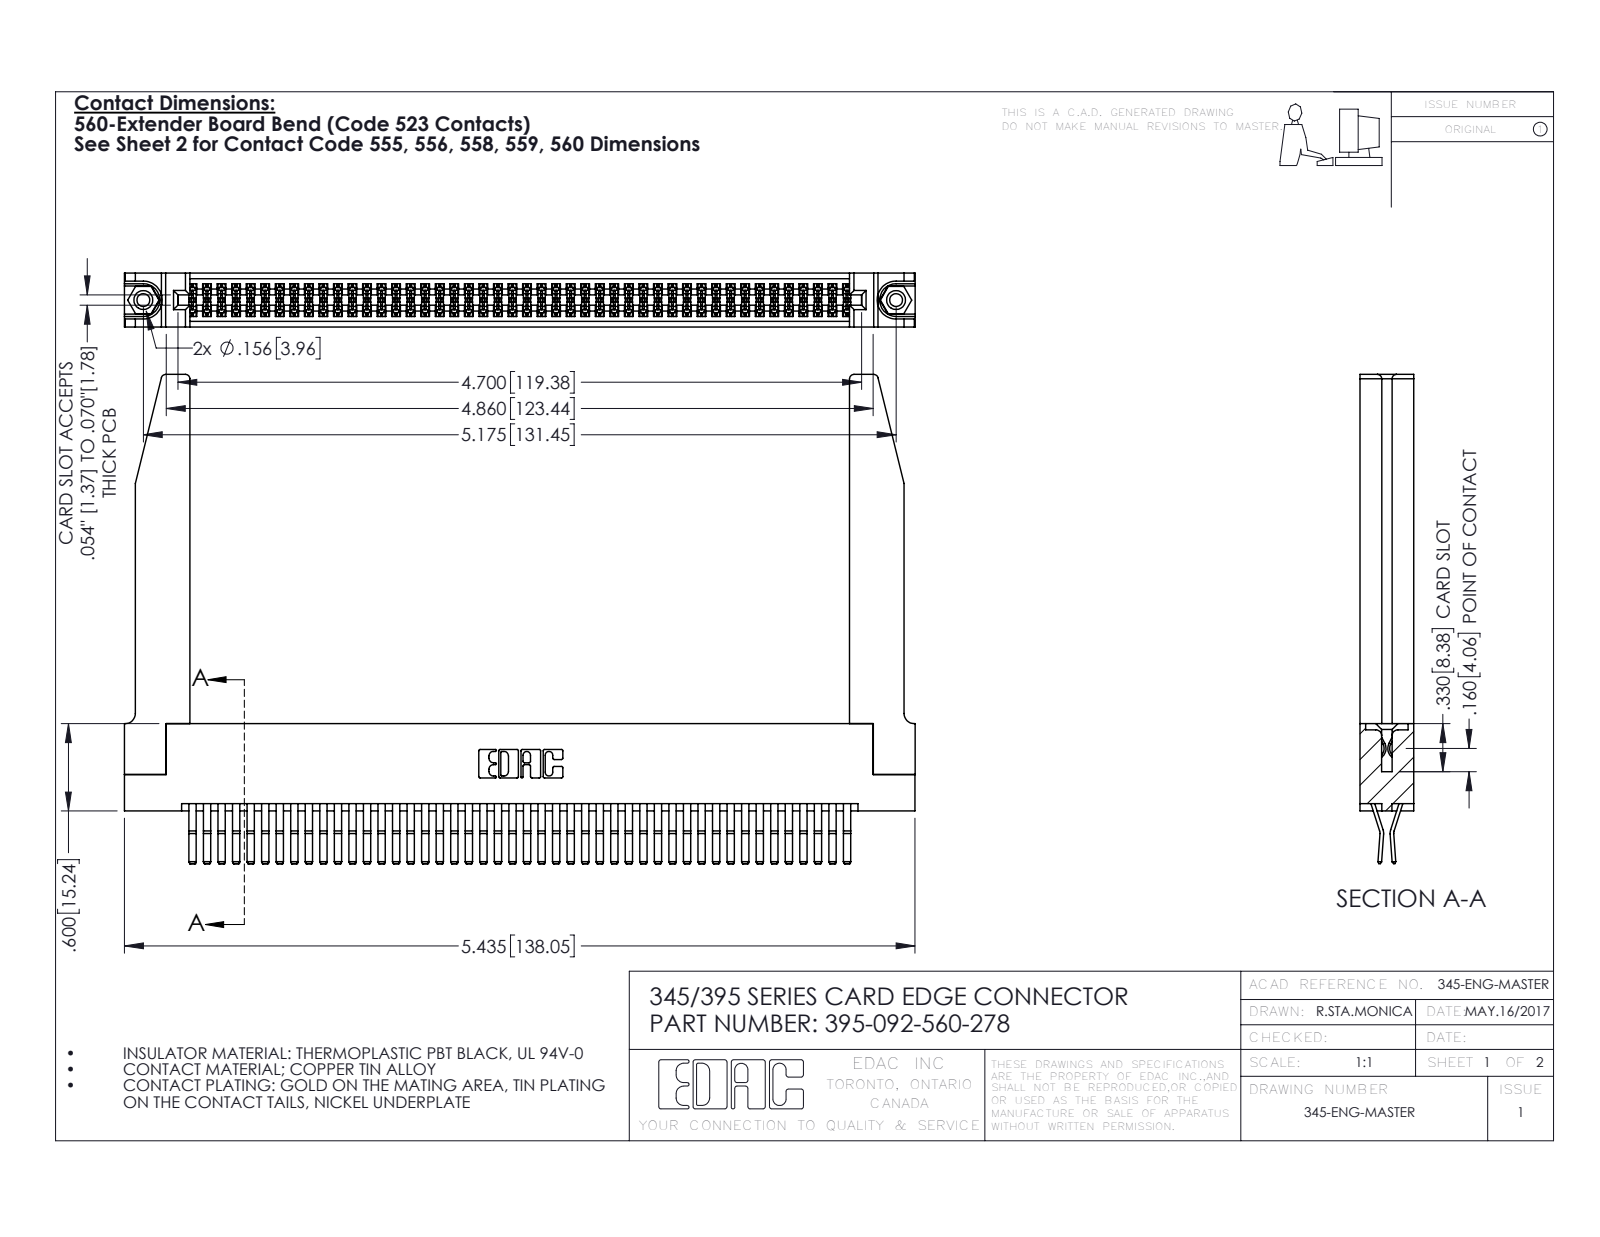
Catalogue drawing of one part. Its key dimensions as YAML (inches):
part_name: "395-092-560-278; 345-220-078_345-220-078; 345-250-001_345-250-001-102; 345-292-001_560 Tail (+1 more)"
step_written_by: "SolidWorks 2016 (CONFIG_CONTROL_DESIGN)"
units: inches
bodies: {solids: 97, faces: 5144, planar: 3258, cylindrical: 1834, other: 52}
overall_size: [5.436, 3.362, 0.37]
volume: 1.332
surface_area: 45.32
round_holes:
  - {diameter: 0.089, count: 2}
  - {diameter: 0.125, count: 2}
  - {diameter: 0.156, count: 2}
  - {diameter: 0.064, count: 1}
round_bosses_or_shafts:
  - {diameter: 0.155, count: 2}
partial_cylinders:
  - {radius: 0.006, count: 138}
  - {radius: 0.01, count: 22}
  - {radius: 0.03, count: 8}
  - {radius: 0.007, count: 6}
  - {radius: 0.031, count: 6}
  - {radius: 0.026, count: 3}
  - {radius: 0.01, count: 2}
  - {radius: 0.014, count: 2}
face_to_face_distances: [0.37, 0.072, 0.298, 0.025, 0.2, 0.098, 0.272, 0.225, 0.148, 0.15]
hole_center_spacings: [0.27, 4.939, 5.175]
